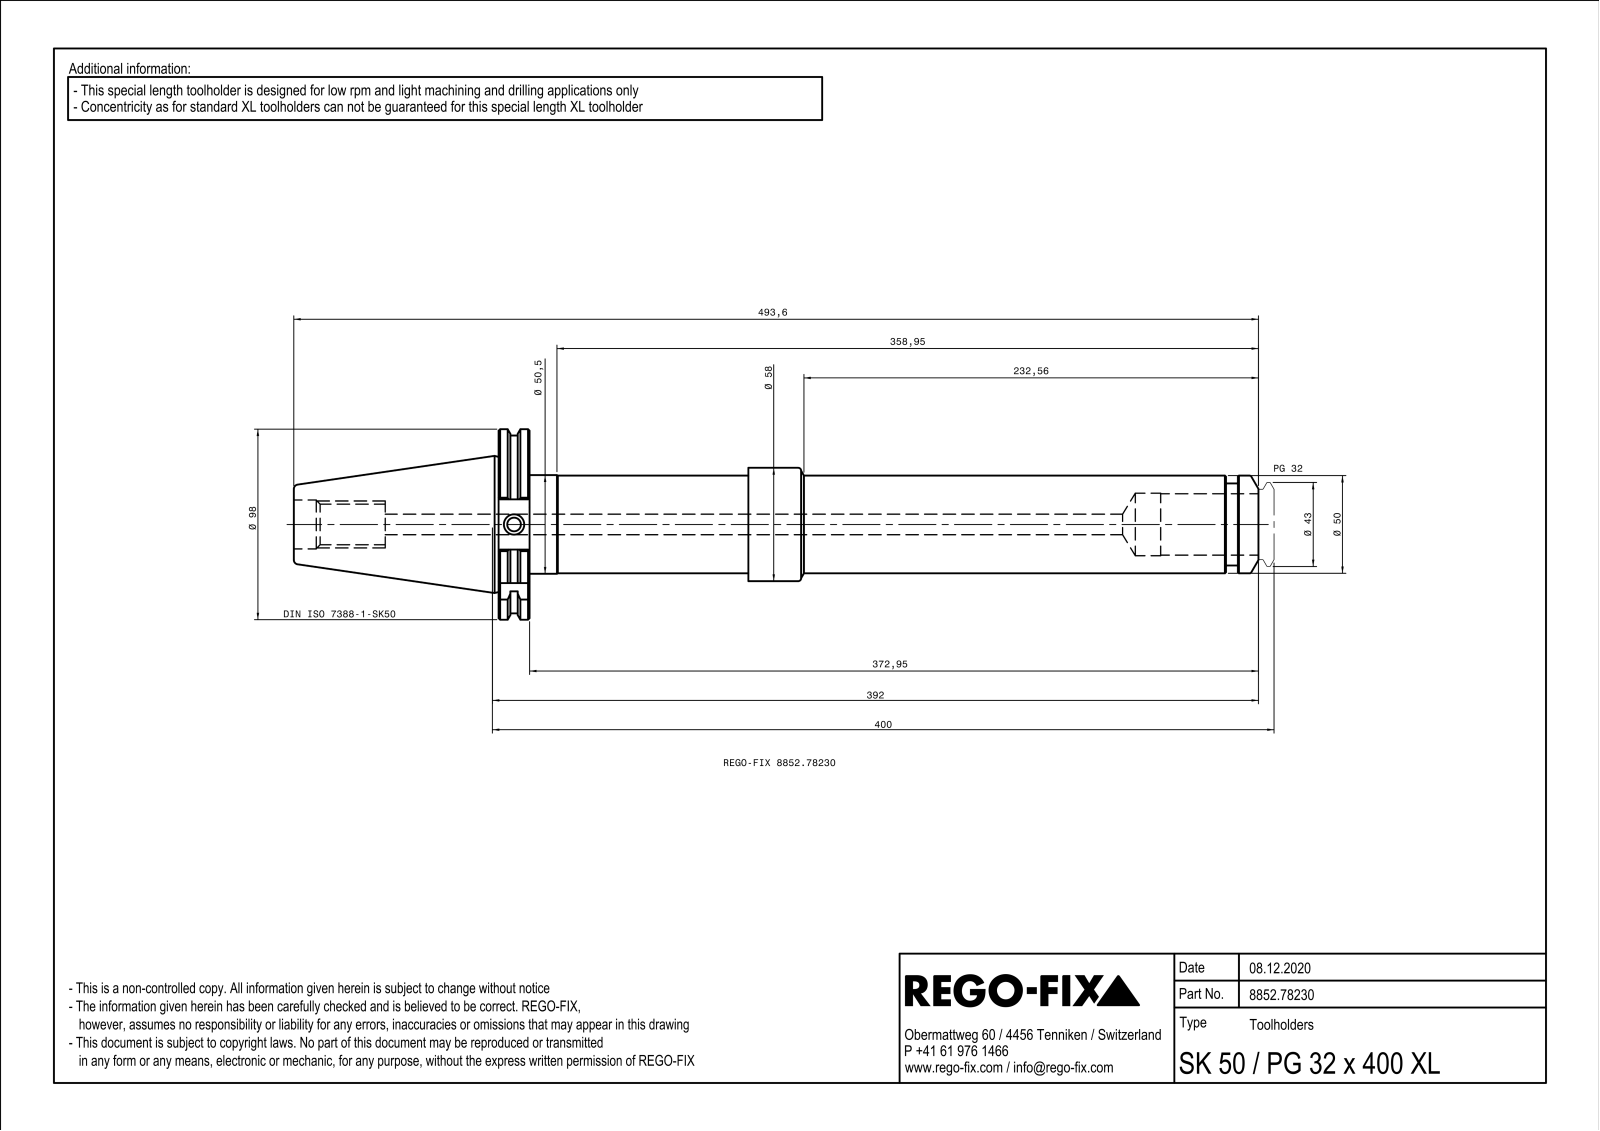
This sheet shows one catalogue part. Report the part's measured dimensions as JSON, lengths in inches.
{"part_name": "NOCUT", "step_written_by": "SIEMENS PLM Software Solid Edge ST10 (AUTOMOTIVE_DESIGN)", "units": "inches", "bodies": {"solids": 1, "faces": 166, "planar": 55, "cylindrical": 39, "other": 72}, "overall_size": [19.433, 3.839, 3.684], "volume_in3": 57.84, "surface_area_in2": 212.3, "round_holes": [[0.276, 1], [0.394, 1], [0.472, 1], [0.551, 1], [0.817, 1], [0.984, 1], [1.299, 1], [2.071, 1], [2.087, 1], [2.102, 1], [2.165, 1]], "round_bosses_or_shafts": [[3.583, 1], [2.283, 1], [1.988, 1], [1.969, 1], [1.654, 1], [1.244, 1], [1.201, 1]], "partial_cylinders_radius": [[0.02, 5], [1.919, 1]], "face_to_face_distances": [0.624, 5.234, 5.858, 9.449, 0.413, 0.24, 0.654, 9.862, 2.323, 2.911]}
